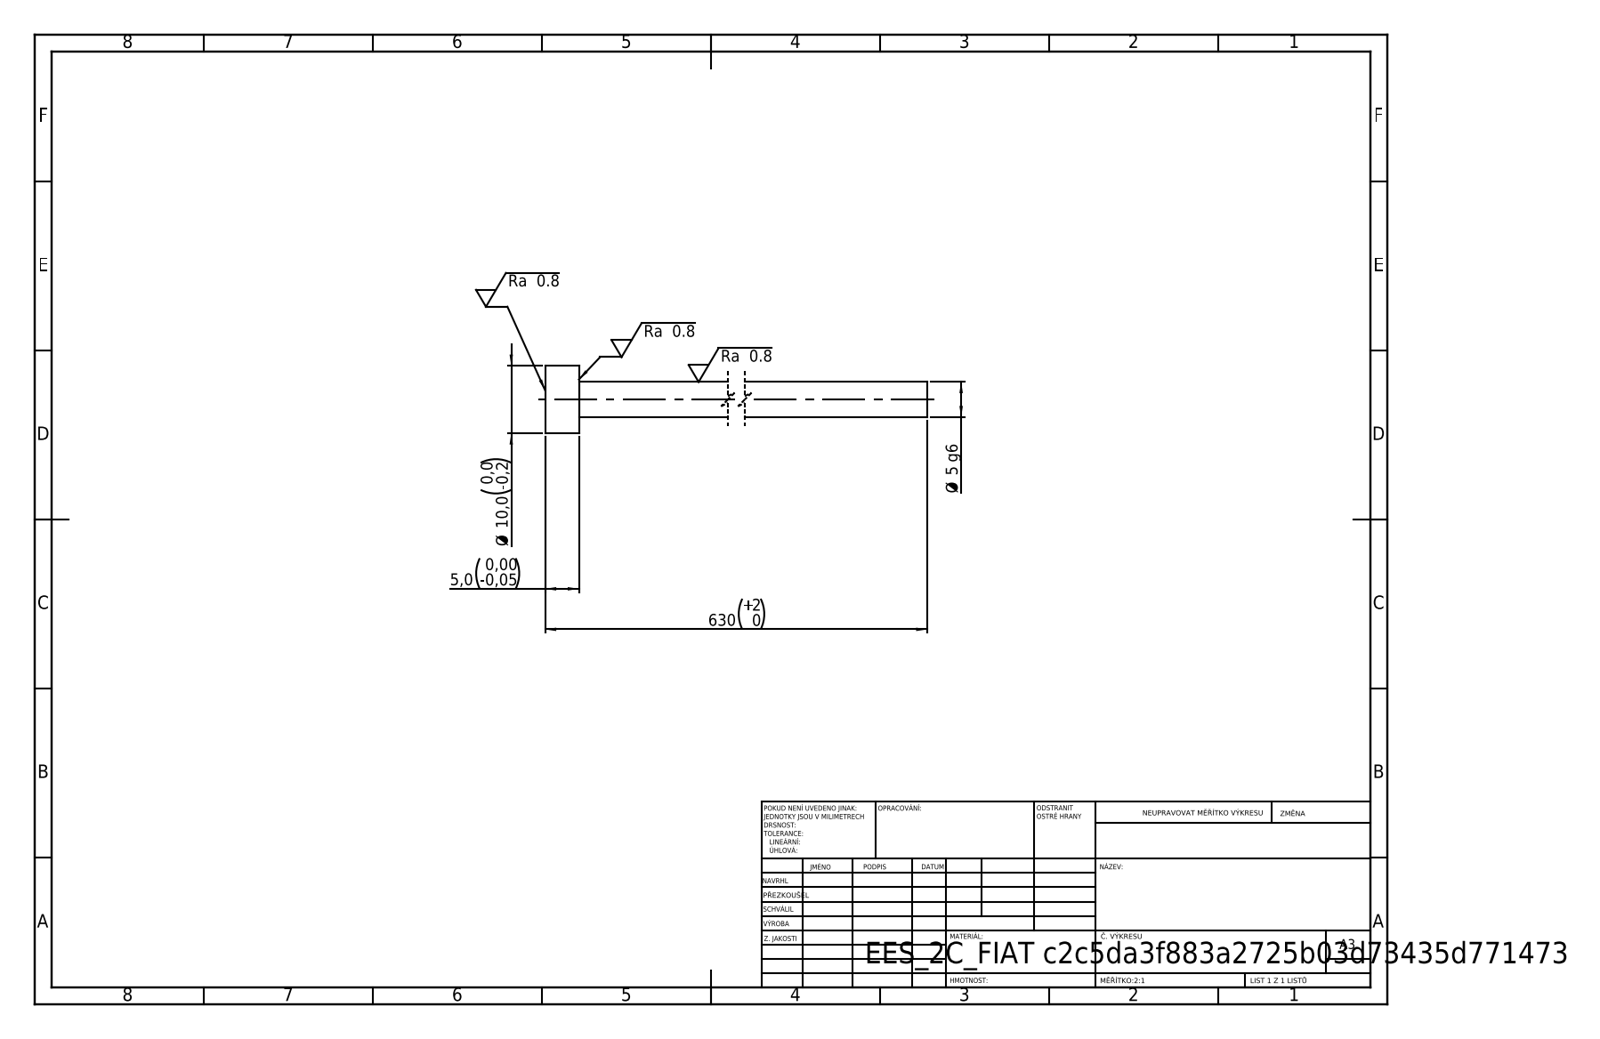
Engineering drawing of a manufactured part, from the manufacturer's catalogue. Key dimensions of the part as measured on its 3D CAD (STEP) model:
STEP written by: SolidWorks 2019 (CONFIG_CONTROL_DESIGN)
Units: millimetres
Bodies: 1 solid, 7 faces (3 planar, 4 cylindrical, 0 other)
Overall size (bounding box): 630 × 10 × 10
Volume: 13 666 mm³ · Surface area: 10 524 mm²
Round bosses / shafts (diameter × count): ⌀10 ×1, ⌀5.2 ×1
Main face-to-face distances: 5, 630, 625
